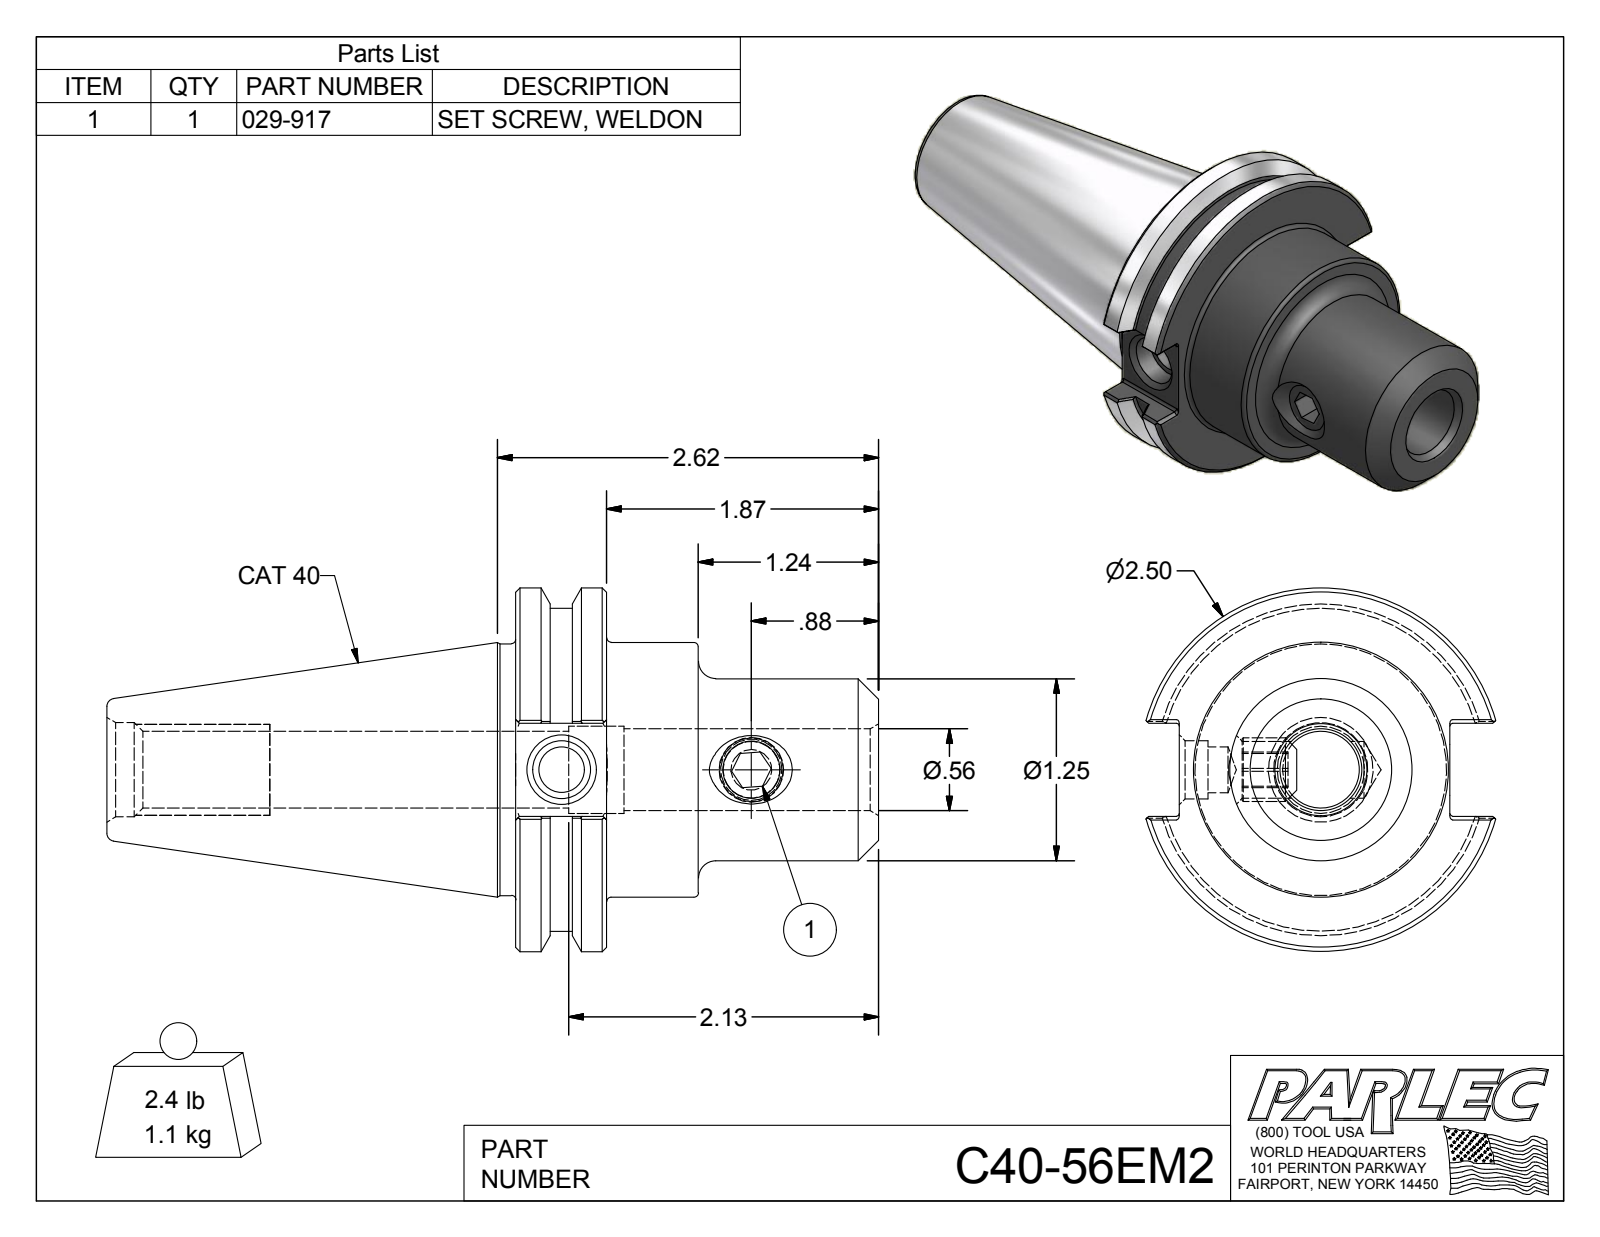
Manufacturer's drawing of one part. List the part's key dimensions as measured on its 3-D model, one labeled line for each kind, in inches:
Part name (STEP PRODUCT): C40-56EM2; C40-56EM2-1; 029-917
STEP written by: Autodesk Inventor 2012 (AUTOMOTIVE_DESIGN)
Units: inches
Bodies: 2 solids, 106 faces (43 planar, 30 cylindrical, 33 other)
Overall size (bounding box): 5.307 × 2.5 × 2.406
Volume: 8.633 in³ · Surface area: 43.56 in²
Round holes (diameter × count): ⌀0.315 ×1, ⌀0.391 ×1, ⌀0.399 ×1, ⌀0.527 ×1, ⌀0.563 ×1, ⌀0.6 ×1, ⌀0.648 ×1
Round bosses / shafts (diameter × count): ⌀2.5 ×1, ⌀2.219 ×1, ⌀1.75 ×1, ⌀1.73 ×1, ⌀1.25 ×1, ⌀0.437 ×1
Partial cylindrical surfaces — rounded edges, fillets, slot ends (radius × count): R0.02 ×12
Main face-to-face distances: 0.625, 1.255, 0.63, 2.495, 1.87, 1.24, 0.236, 0.64, 1.86, 2.812
Hole centre spacings: 1.305
